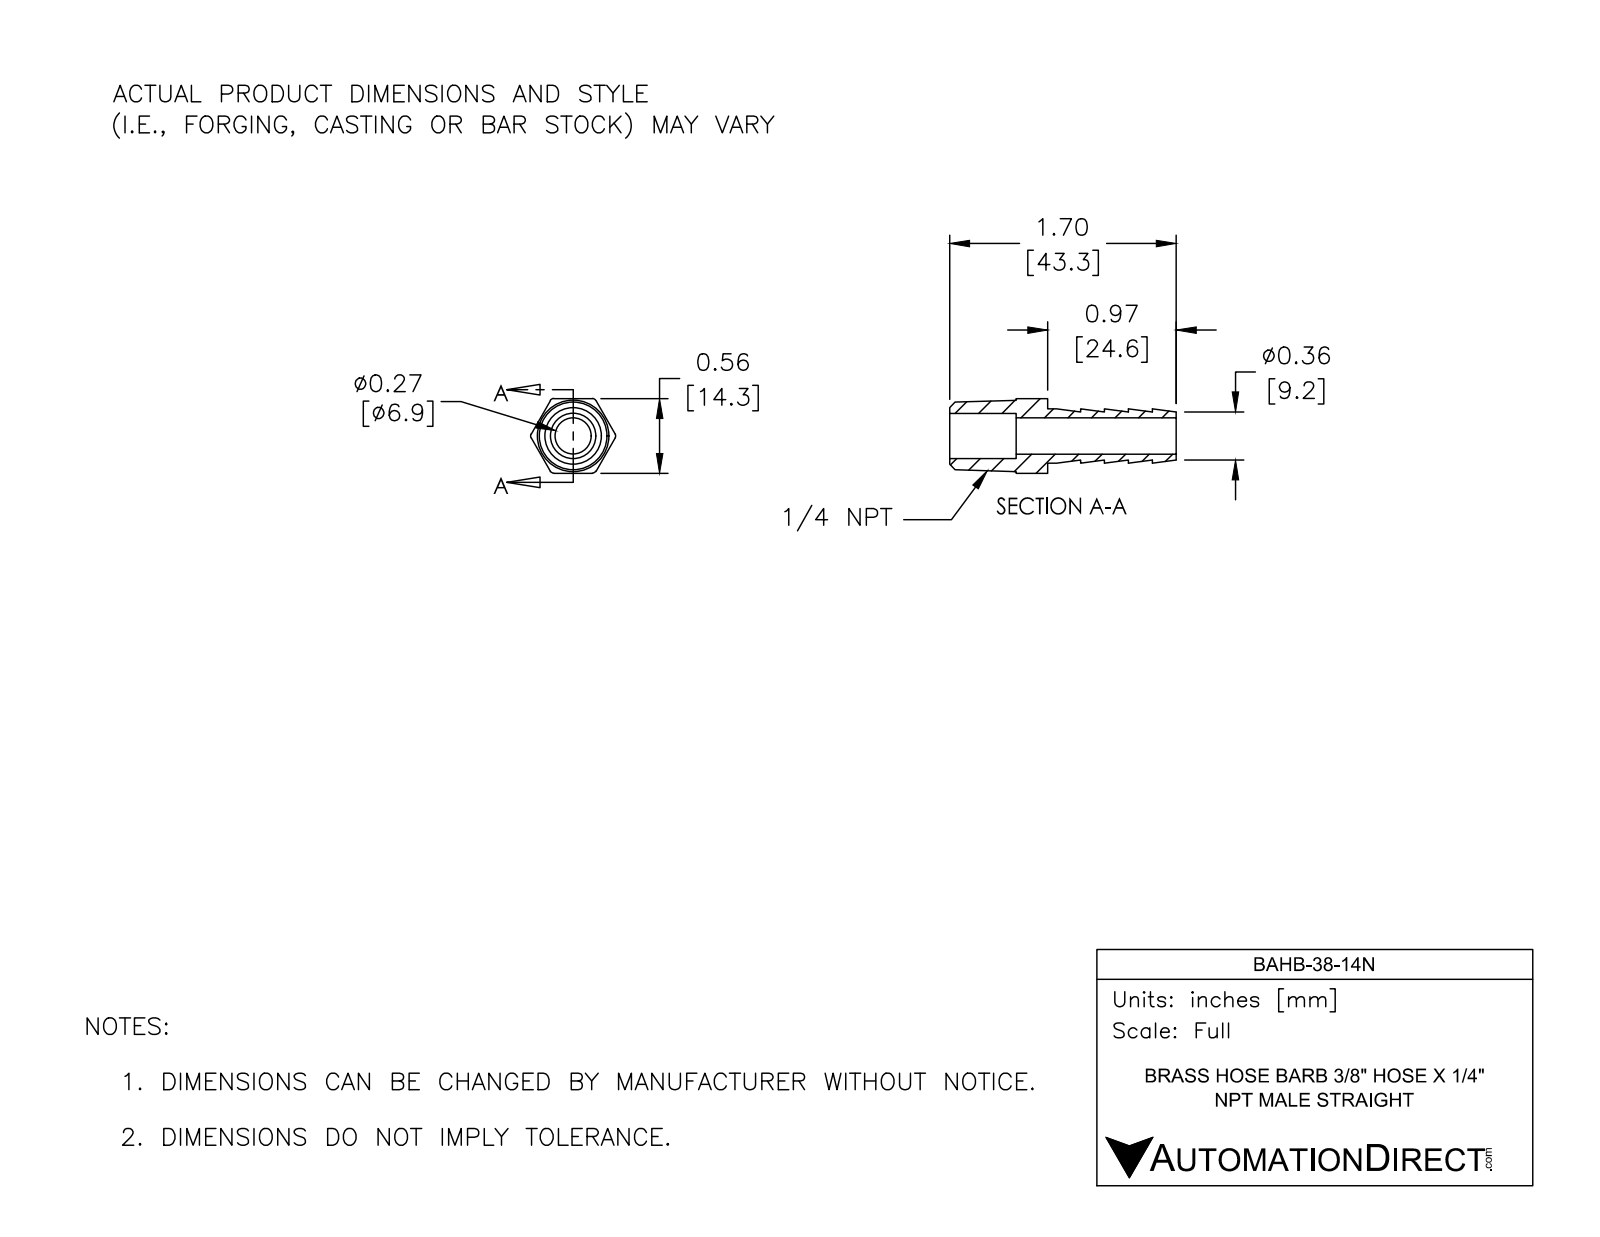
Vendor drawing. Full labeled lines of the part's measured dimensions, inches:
Part name (STEP PRODUCT): BAHB-38-14N
STEP written by: SolidWorks 2017 (AUTOMOTIVE_DESIGN)
Units: inches
Bodies: 1 solid, 41 faces (15 planar, 12 cylindrical, 14 other)
Overall size (bounding box): 1.704 × 0.64 × 0.563
Volume: 0.169 in³ · Surface area: 4.482 in²
Round holes (diameter × count): ⌀0.273 ×1, ⌀0.34 ×1
Round bosses / shafts (diameter × count): ⌀0.409 ×1
Partial cylindrical surfaces — rounded edges, fillets, slot ends (radius × count): R0.03 ×6
Main face-to-face distances: 0.562, 0.18, 0.36, 0.236, 0.54, 0.736, 0.5, 0.968, 1.204, 1.704
